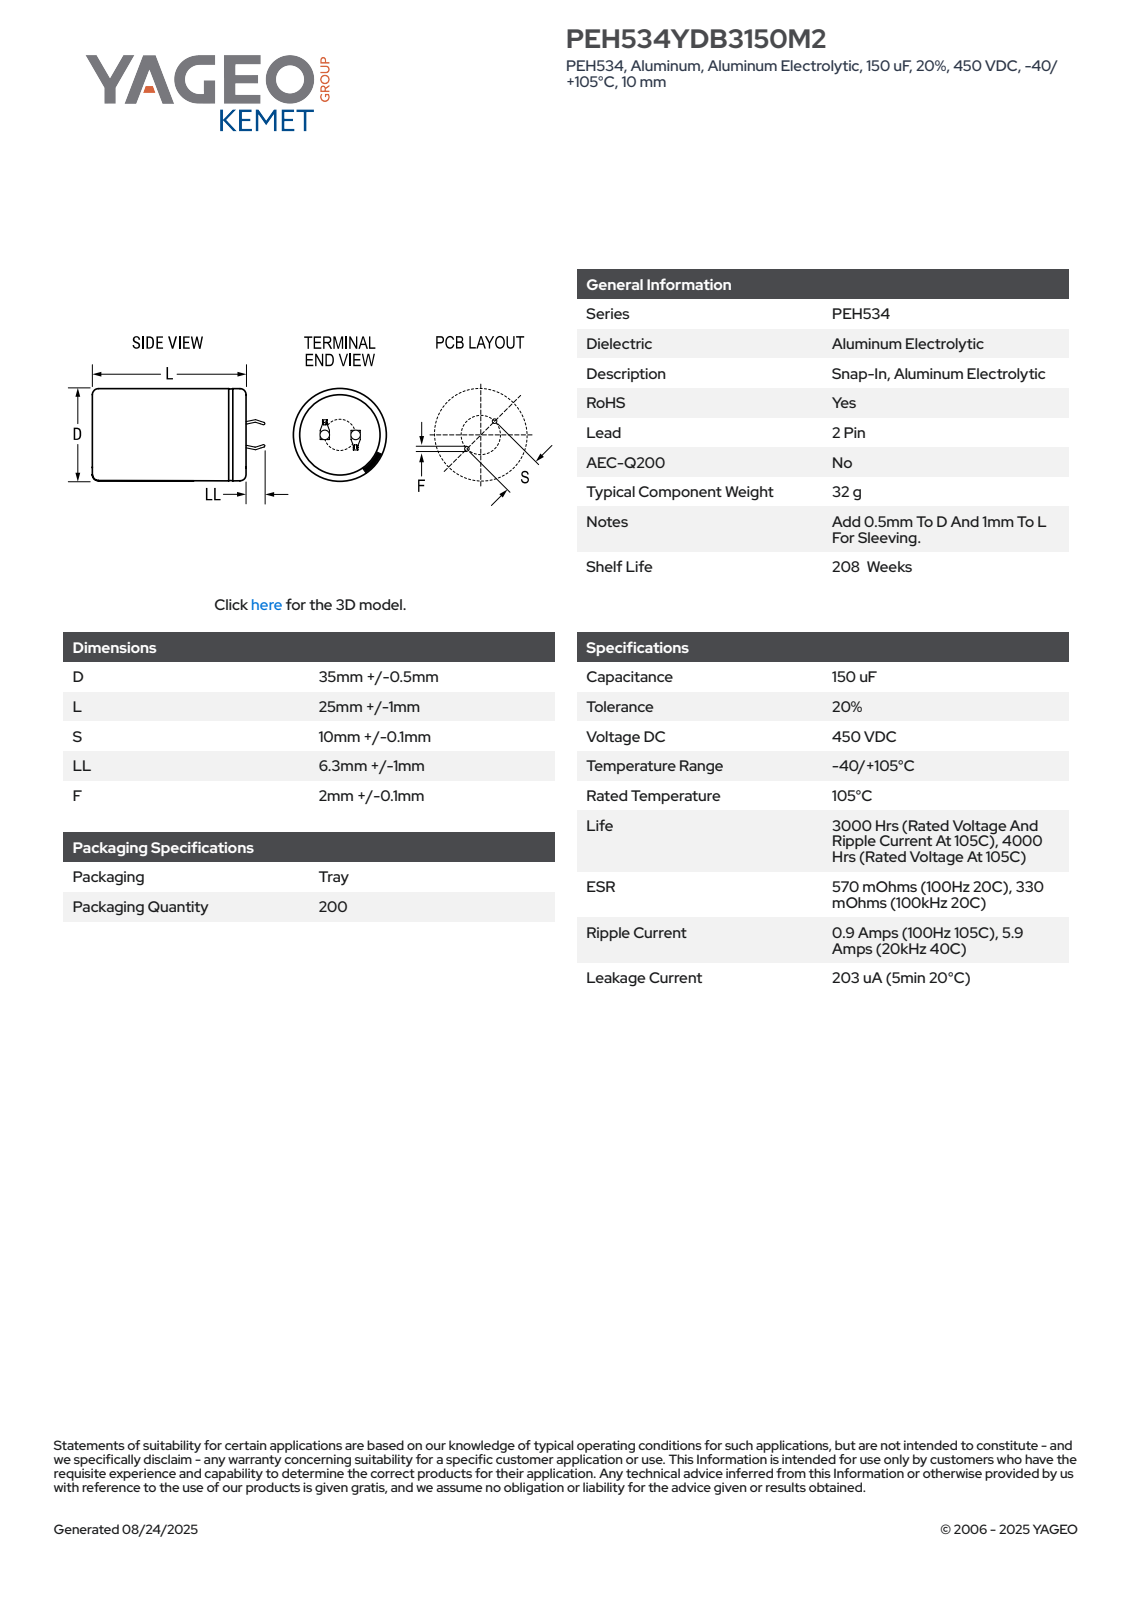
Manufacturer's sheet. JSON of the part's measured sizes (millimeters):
{"part_name": "CARS_K2P_35X25_D35.5L26S10LL7.3F2.1", "step_written_by": "SolidWorks 2014 (AUTOMOTIVE_DESIGN)", "units": "millimeters", "bodies": {"solids": 1, "faces": 100, "planar": 52, "cylindrical": 9, "other": 39}, "overall_size": [35.5, 35.5, 33.29], "volume_mm3": 25229, "surface_area_mm2": 4878, "round_holes": [[31.41, 1]], "round_bosses_or_shafts": [[35.5, 1]], "partial_cylinders_radius": [[17.74, 1]], "face_to_face_distances": [25.99, 0.6, 26.49, 0.5, 7.08, 7.64, 0.75, 1.35, 7.68, 6.48]}
